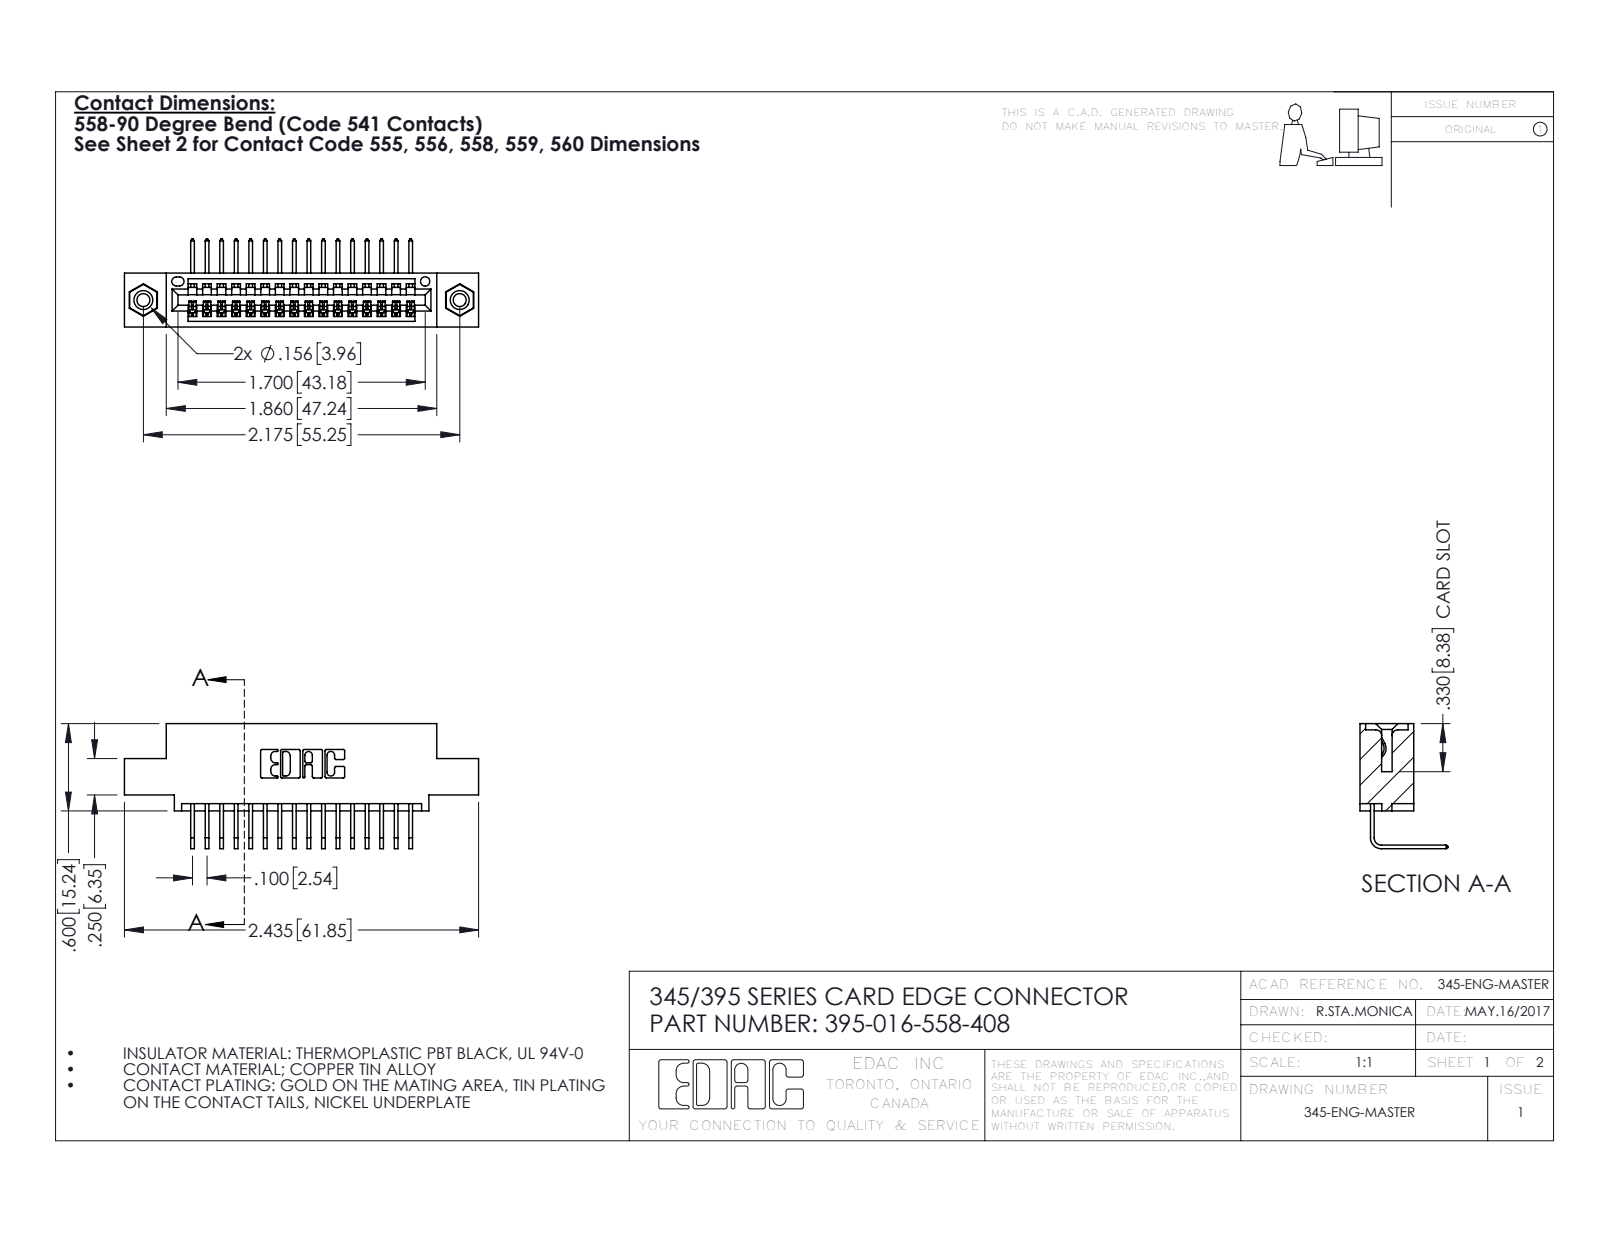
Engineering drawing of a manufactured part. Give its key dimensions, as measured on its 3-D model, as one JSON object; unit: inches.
{"part_name": "345-250-001_345-250-003-102; 345 Part_0.110 Offset - 0.156 Dia-TI; 345-292-001_558 Tail - 2; 395-016-558-408", "step_written_by": "SolidWorks 2016 (CONFIG_CONTROL_DESIGN)", "units": "inches", "bodies": {"solids": 19, "faces": 1150, "planar": 788, "cylindrical": 346, "other": 16}, "overall_size": [2.435, 0.859, 0.605], "volume_in3": 0.344, "surface_area_in2": 11.7, "round_holes": [[0.089, 2], [0.125, 2], [0.156, 2], [0.064, 1]], "round_bosses_or_shafts": [[0.155, 2]], "partial_cylinders_radius": [[0.006, 32], [0.01, 22], [0.007, 6], [0.031, 6], [0.026, 3], [0.031, 2], [0.04, 2], [0.014, 1]], "face_to_face_distances": [0.072, 0.298, 0.37, 0.2, 0.098, 0.272, 0.025, 0.225, 0.1, 0.149], "hole_center_spacings": [0.27, 1.942, 2.175]}
